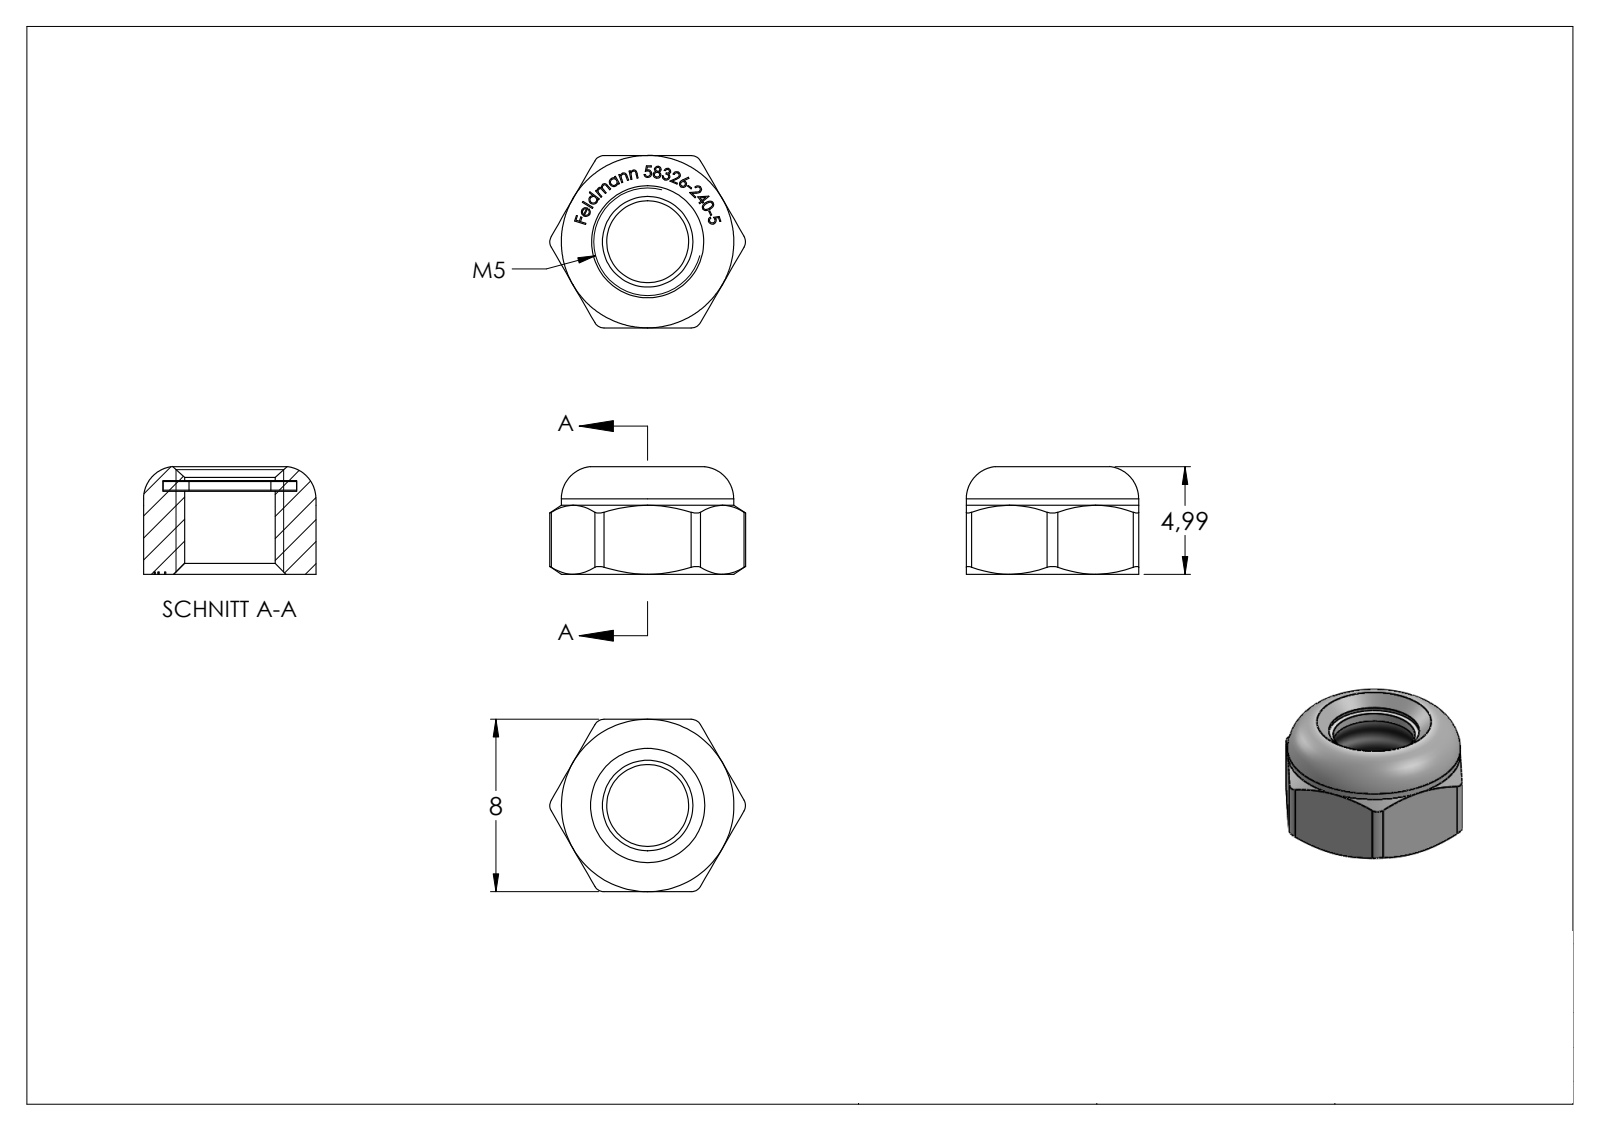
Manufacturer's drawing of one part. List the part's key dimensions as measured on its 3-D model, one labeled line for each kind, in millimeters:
Part name (STEP PRODUCT): 58326-240-5
STEP written by: SolidWorks 2018 (CONFIG_CONTROL_DESIGN)
Units: millimetres
Bodies: 2 solids, 295 faces (143 planar, 12 cylindrical, 140 other)
Overall size (bounding box): 15 × 9.08 × 8
Volume: 181 mm³ · Surface area: 342 mm²
Round holes (diameter × count): ⌀3.8 ×1, ⌀4.2 ×1, ⌀6.2 ×1
Round bosses / shafts (diameter × count): ⌀8 ×1
Partial cylindrical surfaces — rounded edges, fillets, slot ends (radius × count): R0.5 ×6
Main face-to-face distances: 8, 0.45, 0.4, 3.9, 4.3, 3.85, 4.35, 0.5, 3.75, 3.8
